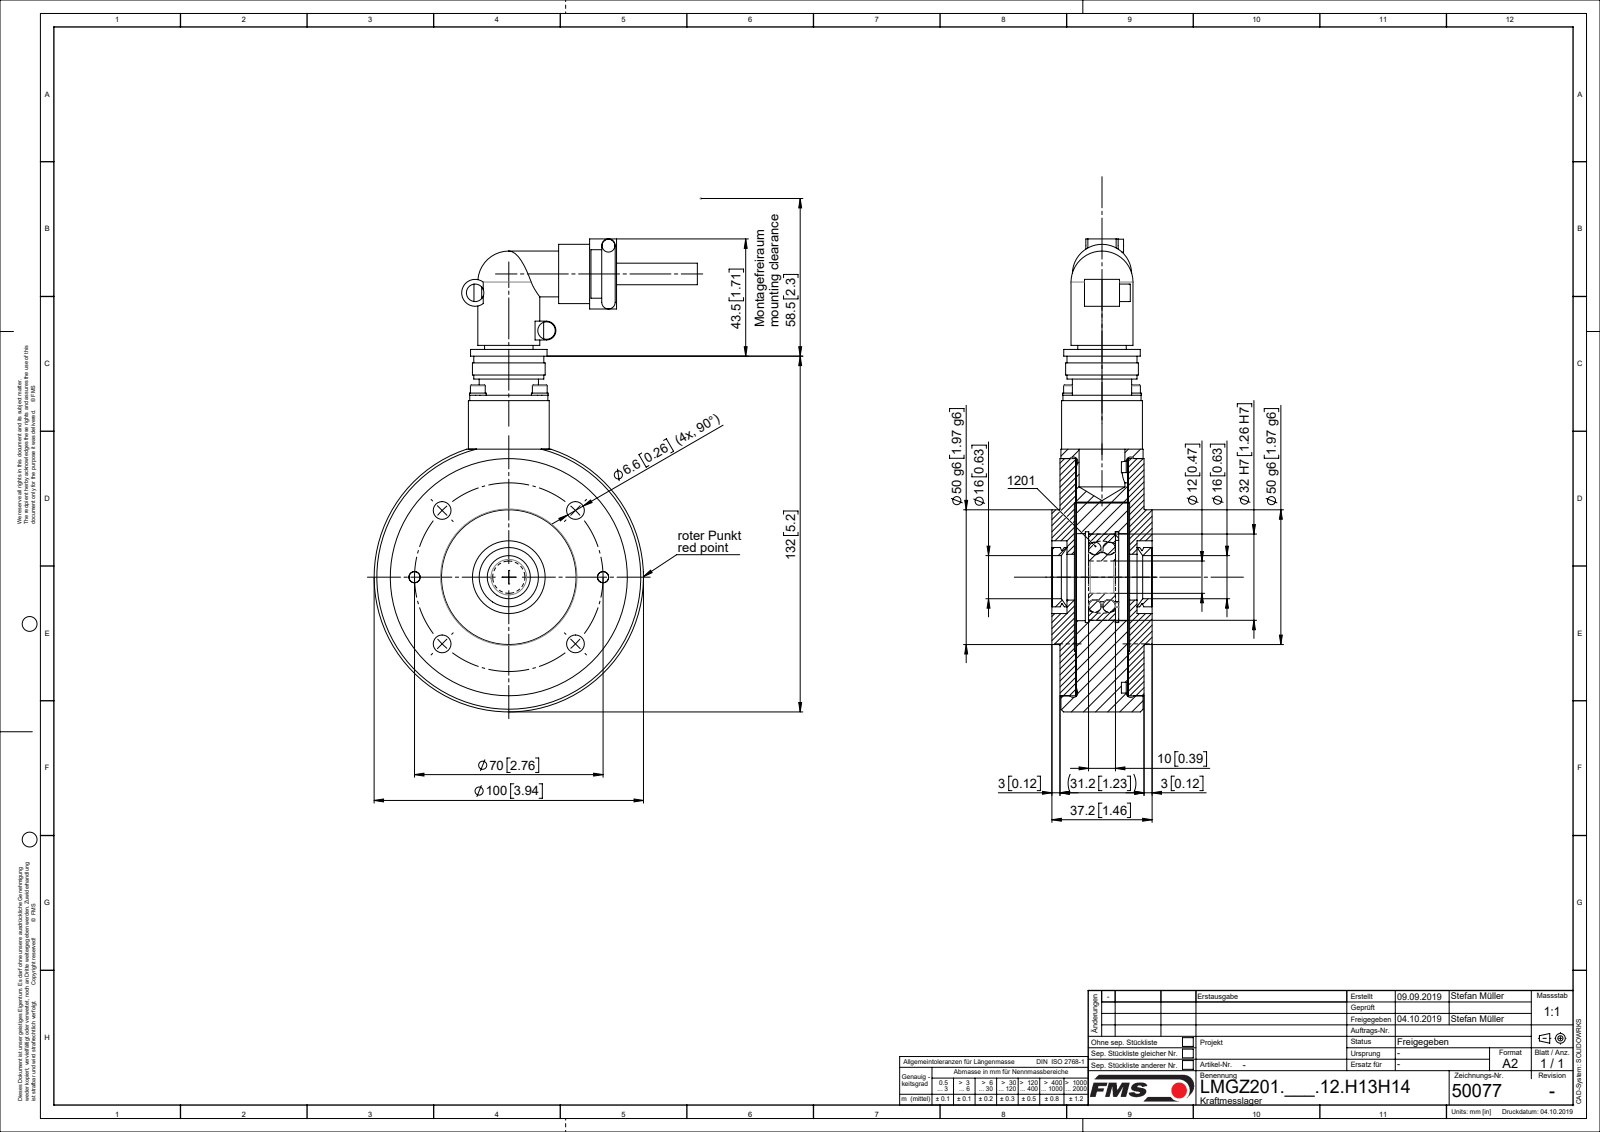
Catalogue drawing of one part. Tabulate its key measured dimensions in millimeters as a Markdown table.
| quantity | value |
| --- | --- |
| part name | L50077; L4866604; TEIL1; L48891 (+8 more) |
| STEP written by | Mechanical Desktop 2007 (CONFIG_CONTROL_DESIGN) |
| units | millimeters |
| bodies | 21 solids, 403 faces (125 planar, 229 cylindrical, 49 other) |
| overall size | 175.5 × 120 × 37.2 |
| volume | 275 382 mm³ |
| surface area | 99 244 mm² |
| round holes (diameter × count) | 6.6 × 7, 2.6 × 4, 3.2 × 4, 3.4 × 4, 3.5 × 4, 4 × 2, 5.5 × 2, 10 × 2, 12 × 1, 16 × 1, 17 × 1, 23 × 1 |
| round bosses / shafts (diameter × count) | 6.2 × 4, 5.5 × 4, 3 × 4, 22 × 3, 8 × 3, 6.5 × 2, 5 × 2, 4.8 × 2 |
| partial cylindrical surfaces (radius × count) | 2.5 × 2, 3.5 × 1, 5 × 1 |
| main face-to-face distances | 19.25, 19, 5.85, 6.1, 25.1, 25.35, 19.5, 20, 5.5, 0.5 |
| hole center spacings | 35, 49.5, 49.51, 26.79, 16.26, 23, 64.67, 70 |
